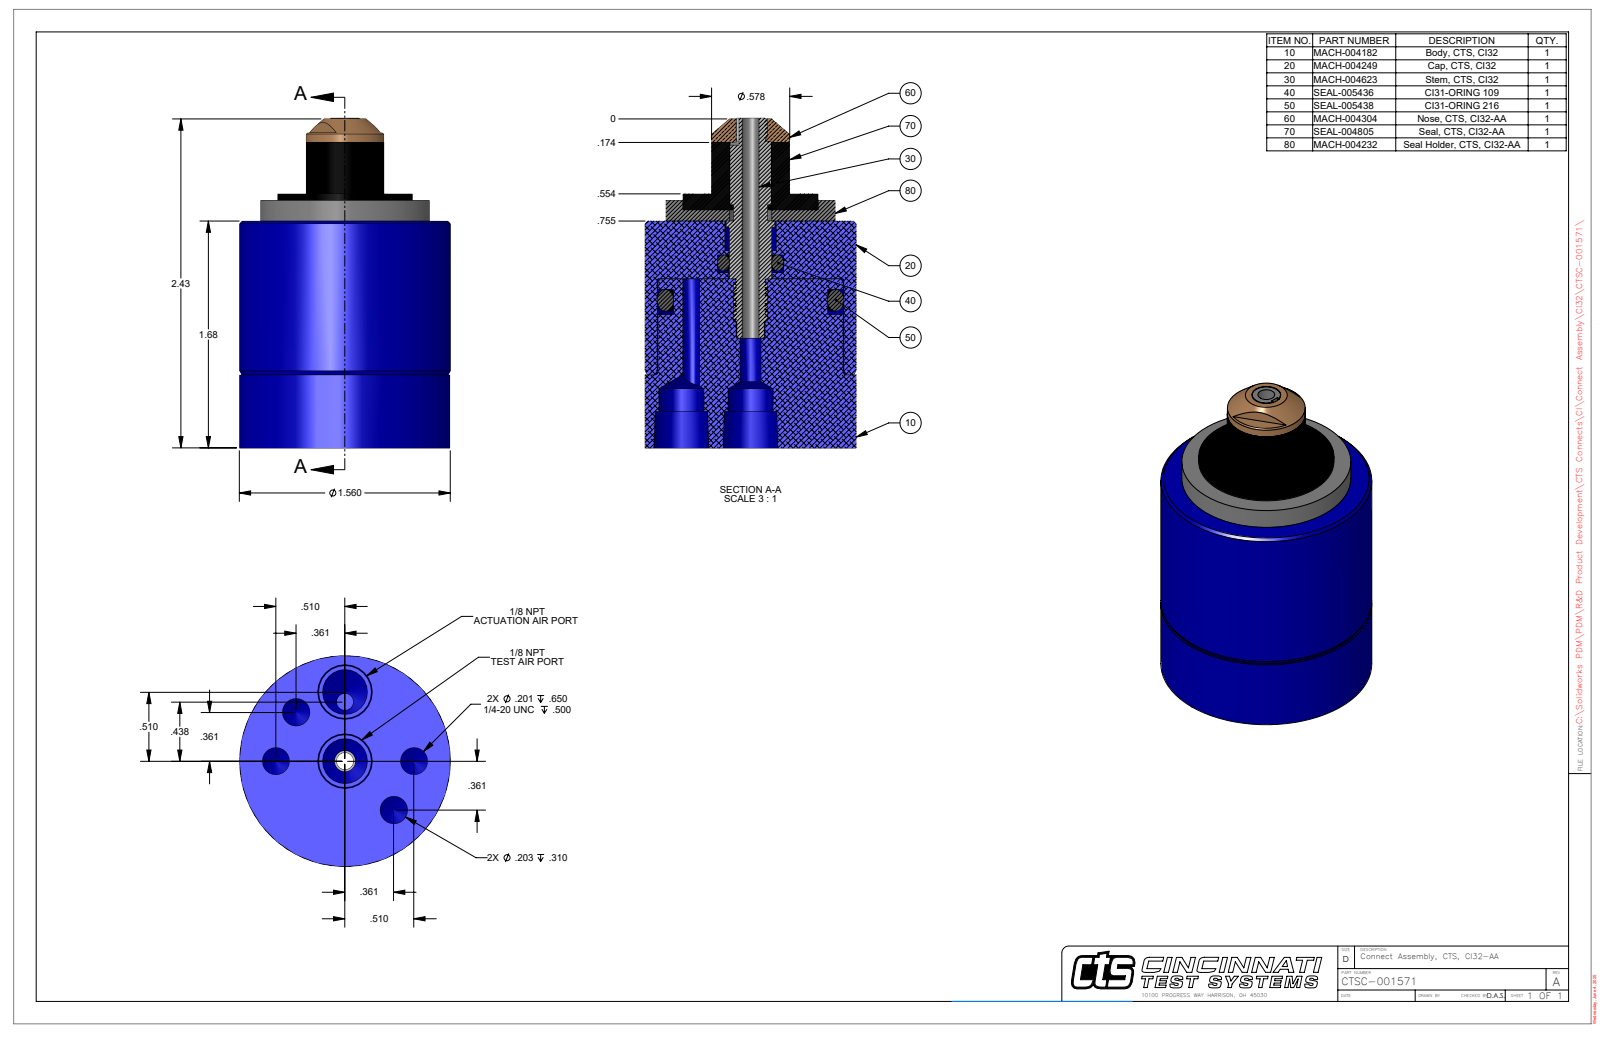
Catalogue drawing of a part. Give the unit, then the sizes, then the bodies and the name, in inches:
Units: inches
Overall size (bounding box): 2.574 × 1.56 × 1.56
Round holes (diameter × count): ⌀0.125 ×2, ⌀0.201 ×2, ⌀0.203 ×2, ⌀0.332 ×2, ⌀0.156 ×1, ⌀0.213 ×1, ⌀1.377 ×1
Round bosses / shafts (diameter × count): ⌀1.56 ×1, ⌀1.365 ×1, ⌀1.25 ×1, ⌀1 ×1, ⌀0.618 ×1, ⌀0.578 ×1, ⌀0.576 ×1
Main face-to-face distances: 1.677, 1.819, 0.141, 2.02, 0.343, 0.201, 1.971, 0.294, 0.152, 0.049
Hole centre spacings: 0.51, 0.39, 0.942, 0.672, 0.721, 0.072, 0.369, 0.437
Volume: 3.394 in³ · Surface area: 21.55 in²
Bodies: 1 solid, 83 faces (19 planar, 38 cylindrical, 26 other)
Part name (STEP PRODUCT): CTSC-001571
STEP written by: SolidWorks 2023 (AUTOMOTIVE_DESIGN)
